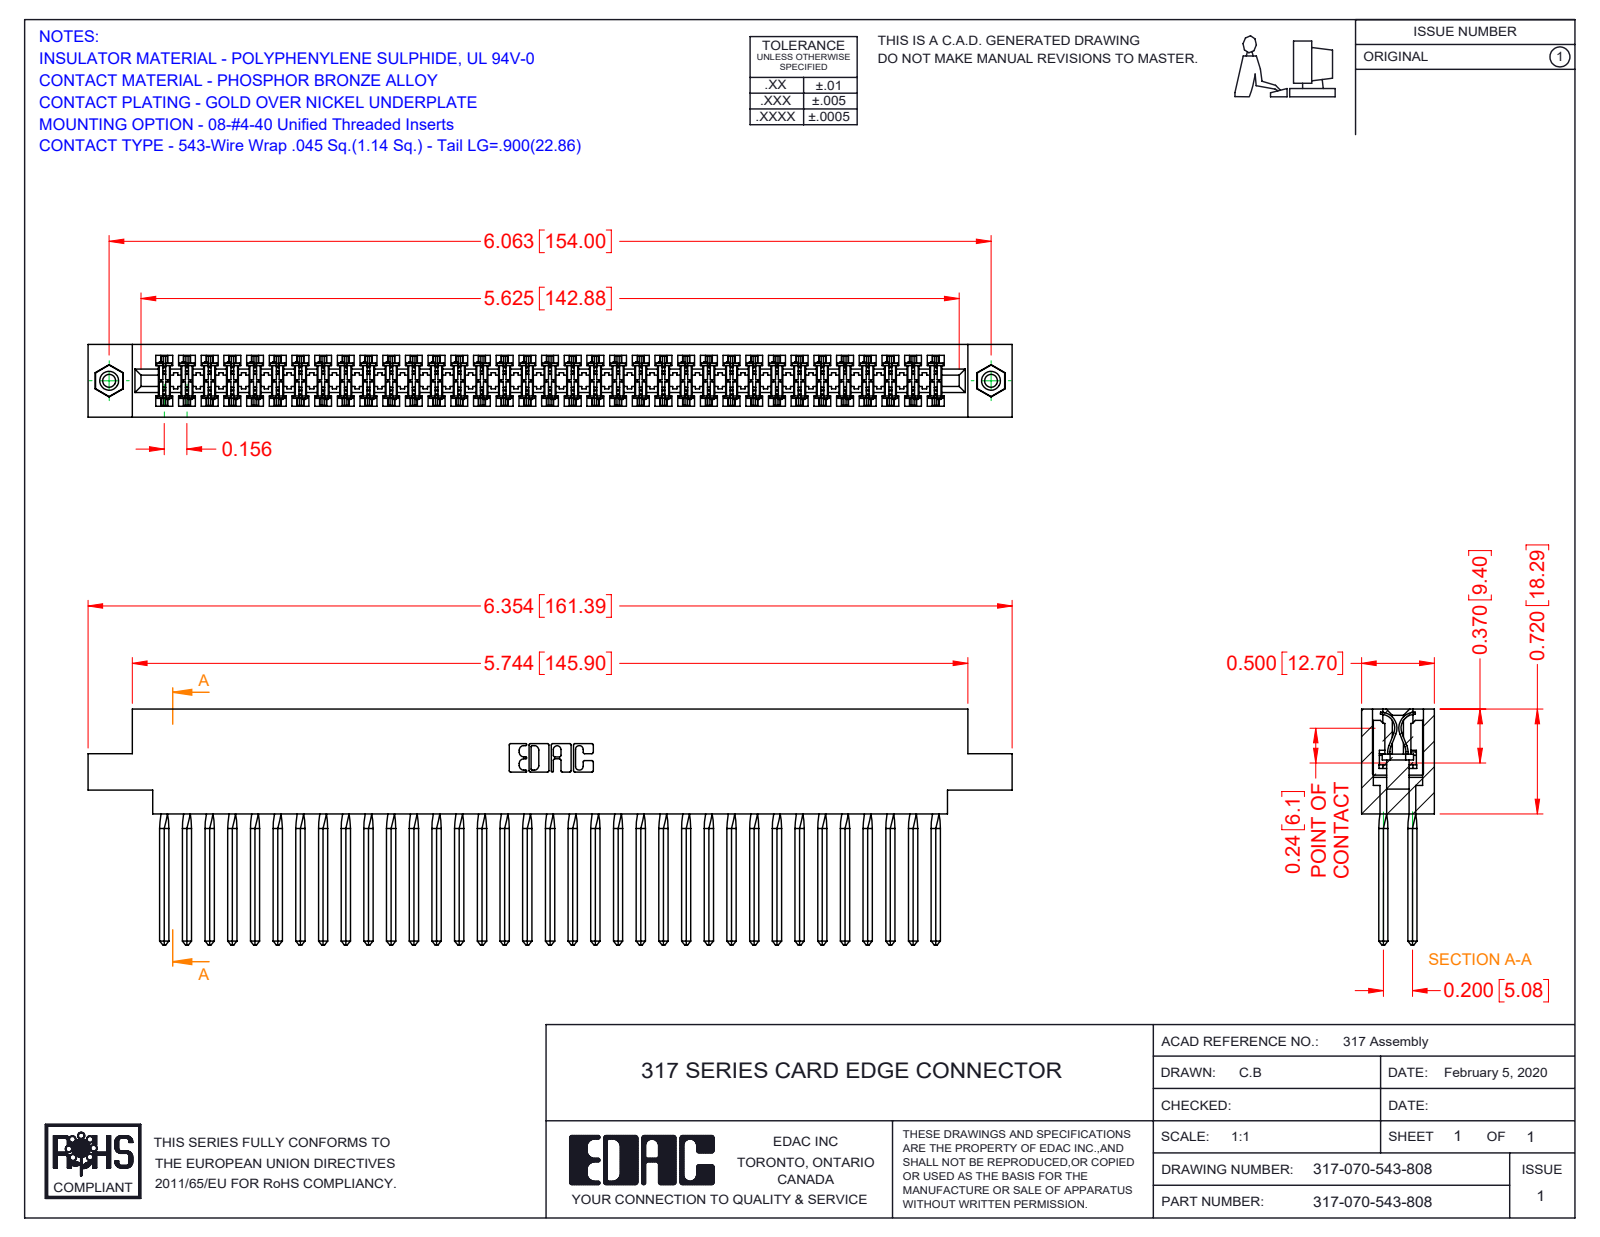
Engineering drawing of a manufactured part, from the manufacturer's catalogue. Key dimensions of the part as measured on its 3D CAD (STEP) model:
Part name (STEP PRODUCT): 345-250-001_345-250-003-102; 317 Part_.156 Dia - TI; 317-070-543-878; 317-290-001_543
STEP written by: SolidWorks 2016 (CONFIG_CONTROL_DESIGN)
Units: inches
Bodies: 73 solids, 6392 faces (5200 planar, 896 cylindrical, 296 other)
Overall size (bounding box): 6.354 × 1.62 × 0.5
Volume: 1.659 in³ · Surface area: 63.55 in²
Round holes (diameter × count): ⌀0.089 ×2, ⌀0.125 ×2, ⌀0.156 ×2
Round bosses / shafts (diameter × count): ⌀0.155 ×2
Partial cylindrical surfaces — rounded edges, fillets, slot ends (radius × count): R0.015 ×140, R0.01 ×22, R0.007 ×6, R0.031 ×6, R0.026 ×3, R0.095 ×2, R0.1 ×2, R0.11 ×2
Main face-to-face distances: 0.5, 0.075, 0.425, 0.35, 0.11, 0.195, 0.094, 0.2, 0.115, 0.131
Hole centre spacings: 6.063
